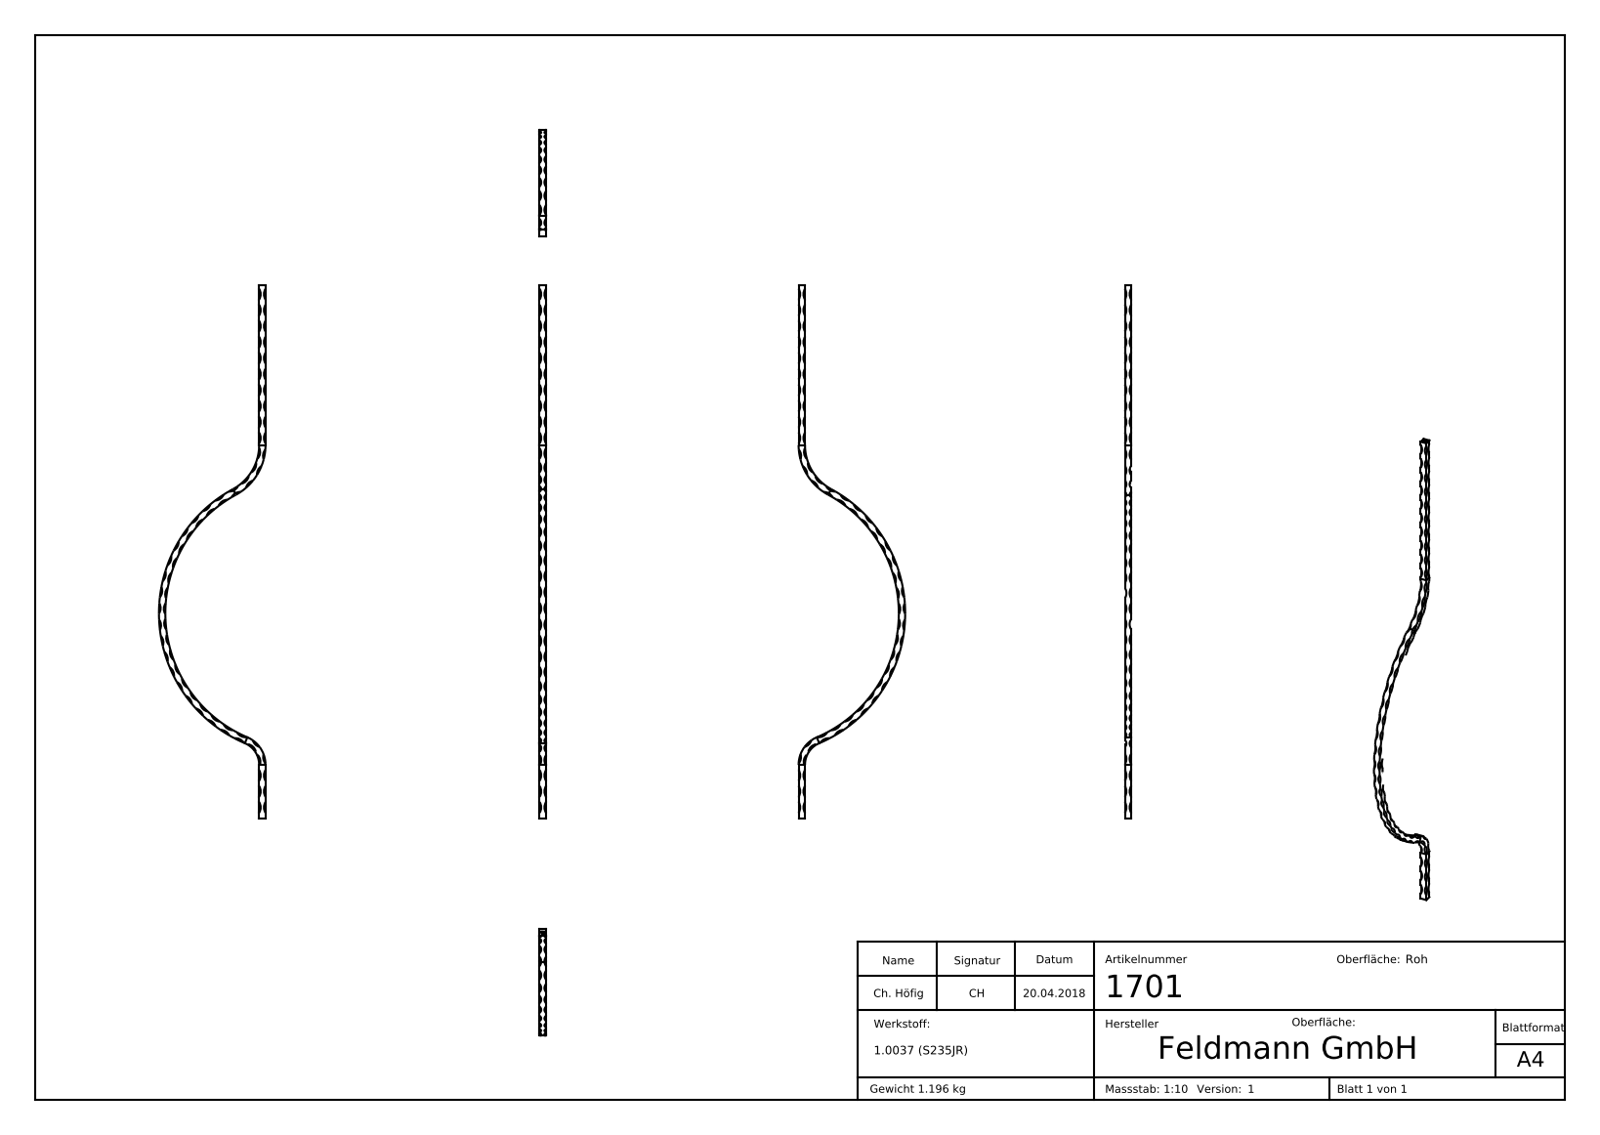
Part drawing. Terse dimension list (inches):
name: 1701
written by: SolidWorks 2015 (CONFIG_CONTROL_DESIGN)
unit: in
bodies: 1 solid, 323 faces (106 planar, 8 cylindrical, 209 other)
size: 39.37 × 7.874 × 0.709
volume: 9.812 in³; area: 87.01 in²
rounds: 1× R1.732, 1× R2.205, 1× R3.701, 1× R4.173, 1× R9.961, 1× R10.433
face distances: 0.472, 39.37, 39.366, 0.147, 0.022, 0.106, 0.144, 0.152, 0.236, 0.015
